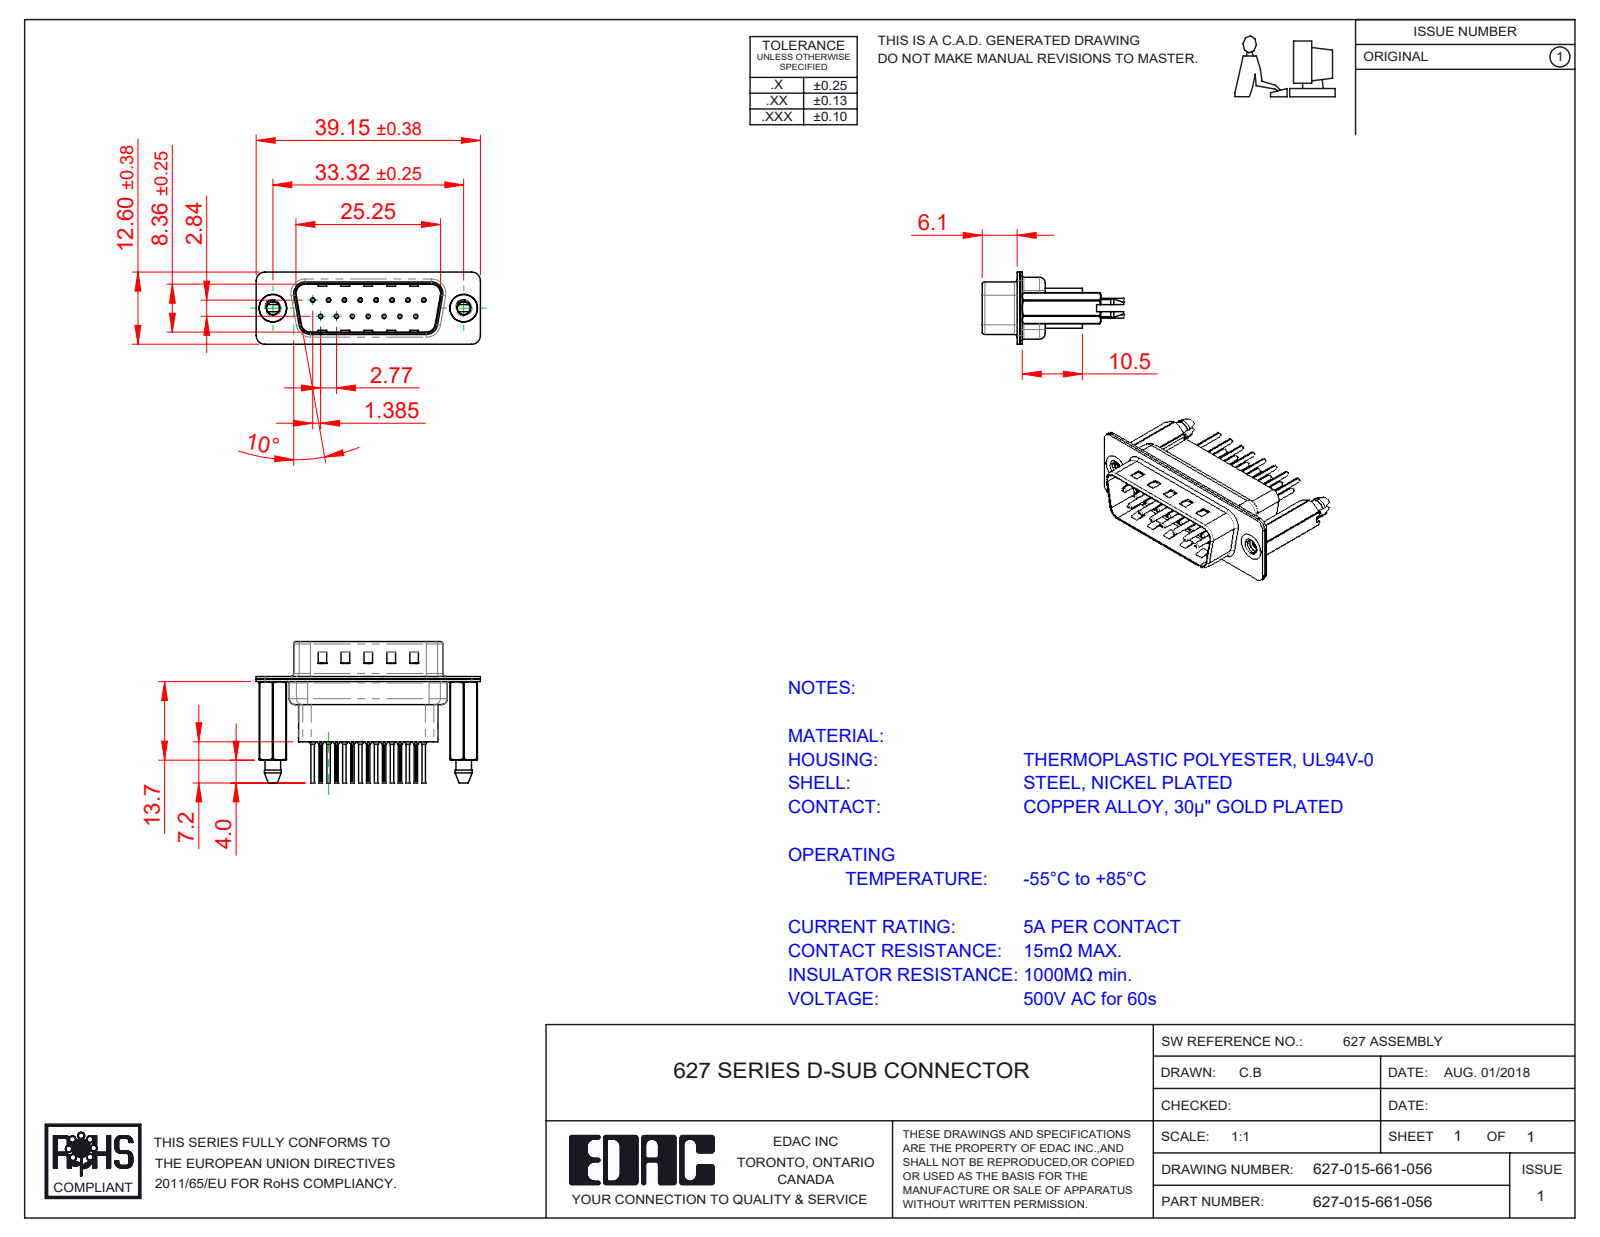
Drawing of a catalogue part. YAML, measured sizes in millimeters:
part_name: "627-015-661-056; 627 Contact Row 2_61; 627 4-40 Threaded Boardlock_HP61; 627 Shell Front_15 Contacts (+3 more)"
step_written_by: "SolidWorks 2020 (CONFIG_CONTROL_DESIGN)"
units: millimeters
bodies: {solids: 20, faces: 1918, planar: 531, cylindrical: 754, other: 633}
overall_size: [39.15, 24.6, 12.6]
volume: 2896
surface_area: 7494
round_holes:
  - {diameter: 0.2, count: 15}
  - {diameter: 0.35, count: 15}
  - {diameter: 1.1, count: 15}
  - {diameter: 1.6, count: 15}
  - {diameter: 2.26, count: 2}
  - {diameter: 4, count: 2}
  - {diameter: 4.8, count: 2}
round_bosses_or_shafts:
  - {diameter: 2, count: 15}
  - {diameter: 1.5, count: 15}
  - {diameter: 0.75, count: 15}
  - {diameter: 0.6, count: 15}
  - {diameter: 4.9, count: 2}
partial_cylinders:
  - {radius: 0.1, count: 30}
  - {radius: 1.5, count: 18}
  - {radius: 2, count: 12}
  - {radius: 1.6, count: 10}
  - {radius: 0.5, count: 8}
  - {radius: 0.25, count: 4}
  - {radius: 0.6, count: 4}
  - {radius: 0.65, count: 4}
face_to_face_distances: [0.4, 0.45, 0.9, 0.82, 9.58, 1.5, 0.68, 4.76, 7.68, 1.4]
hole_center_spacings: [3.16, 2.77, 5.54, 8.31, 11.08, 5.03, 5.04, 7.48]
